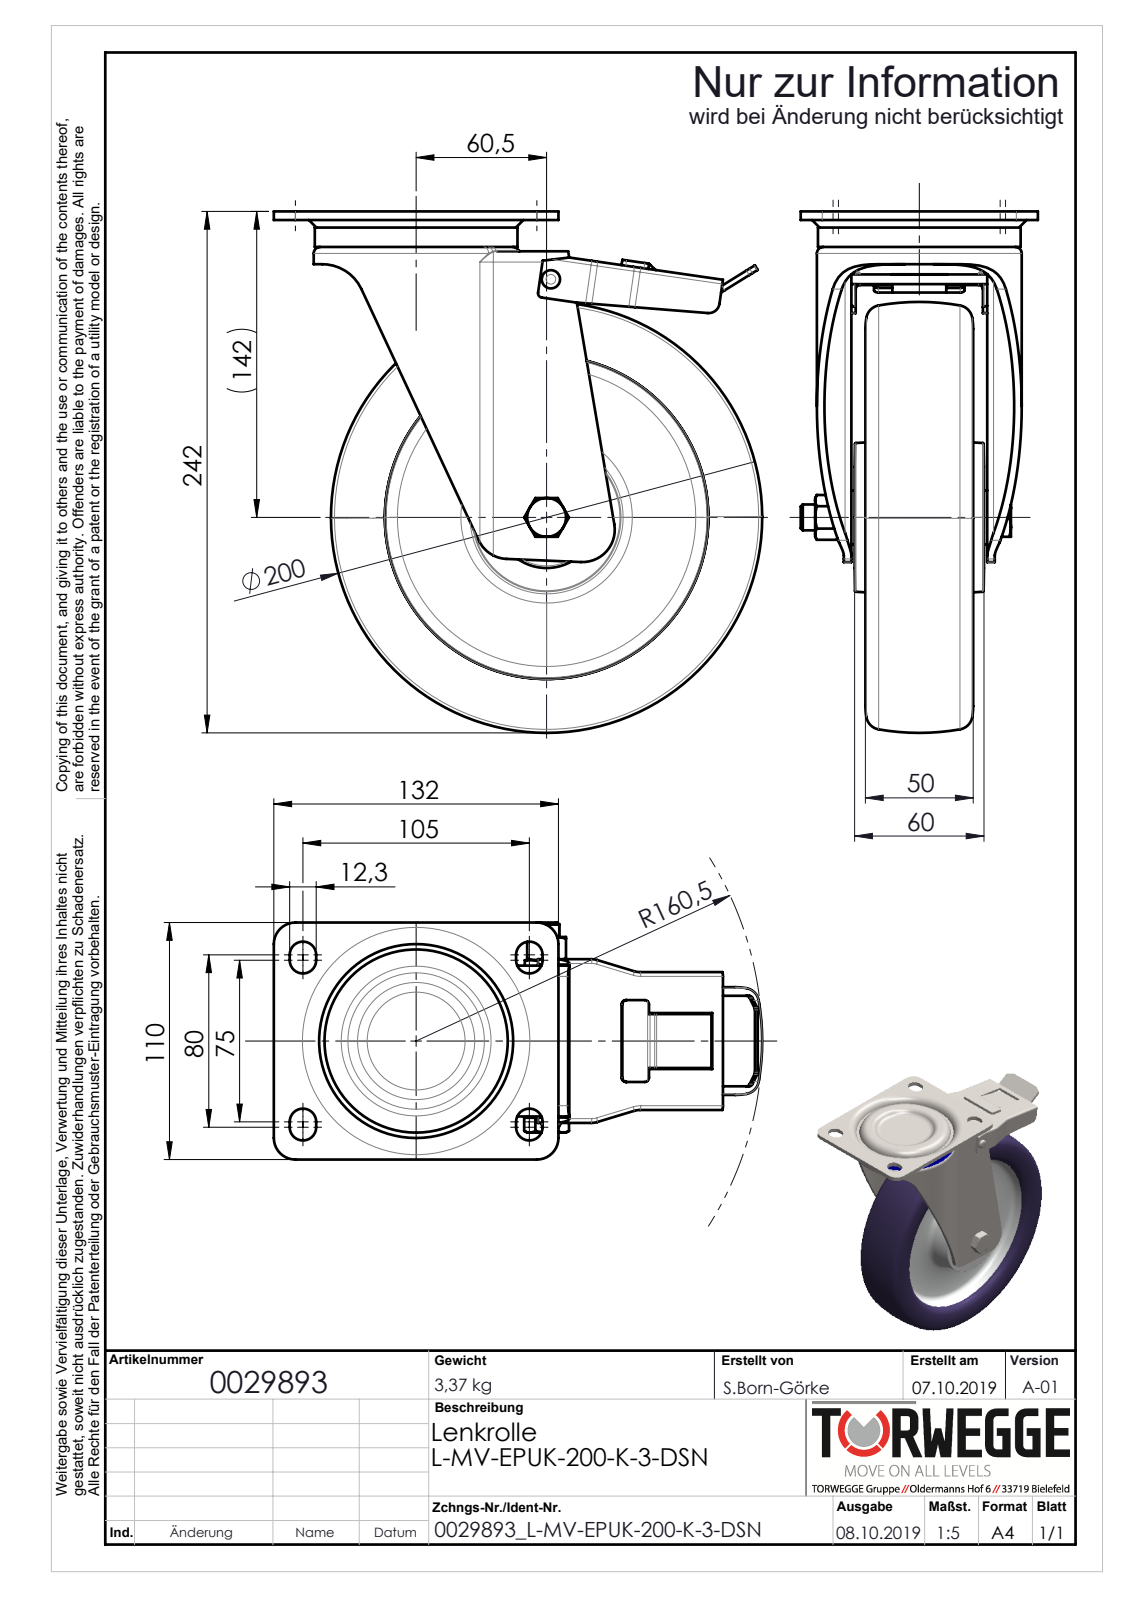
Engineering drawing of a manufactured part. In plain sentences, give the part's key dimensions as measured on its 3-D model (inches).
The part is named "0029893_L-MV-EPUK-200-K-3-DSN_(A-01)". Its 3-D file was written by "SolidWorks 2018 (AUTOMOTIVE_DESIGN)". It is 13 solids with 564 faces: 180 planar, 171 cylindrical and 213 other. Overall it measures 9.463 by 8.917 by 4.331 inches. Its volume is 78.42 cubic inches and its surface area 551.8 square inches. Round holes: 1 of diameter 0.197, 1 of diameter 0.402, 1 of diameter 0.472, 1 of diameter 0.48, 1 of diameter 0.492, 1 of diameter 0.787, 1 of diameter 0.827, 1 of diameter 1.378, 1 of diameter 1.531. Round bosses or shafts: 1 of diameter 3.701, 1 of diameter 1.85, 1 of diameter 1.106, 1 of diameter 0.984, 1 of diameter 0.795, 1 of diameter 0.783, 1 of diameter 0.709, 1 of diameter 0.335. Partial cylindrical surfaces (rounded edges, fillets, slot ends): 26 of radius 0.079, 14 of radius 0.394, 8 of radius 0.242, 3 of radius 0.197, 2 of radius 0.059, 2 of radius 0.531, 2 of radius 0.591, 1 of radius 0.787. The main face-to-face distances are 0.138, 2.618, 0.551, 0.63, 0.059, 0.689, 2.067, 1.929, 0.079, 0.098. The hole center spacings are 4.351.
